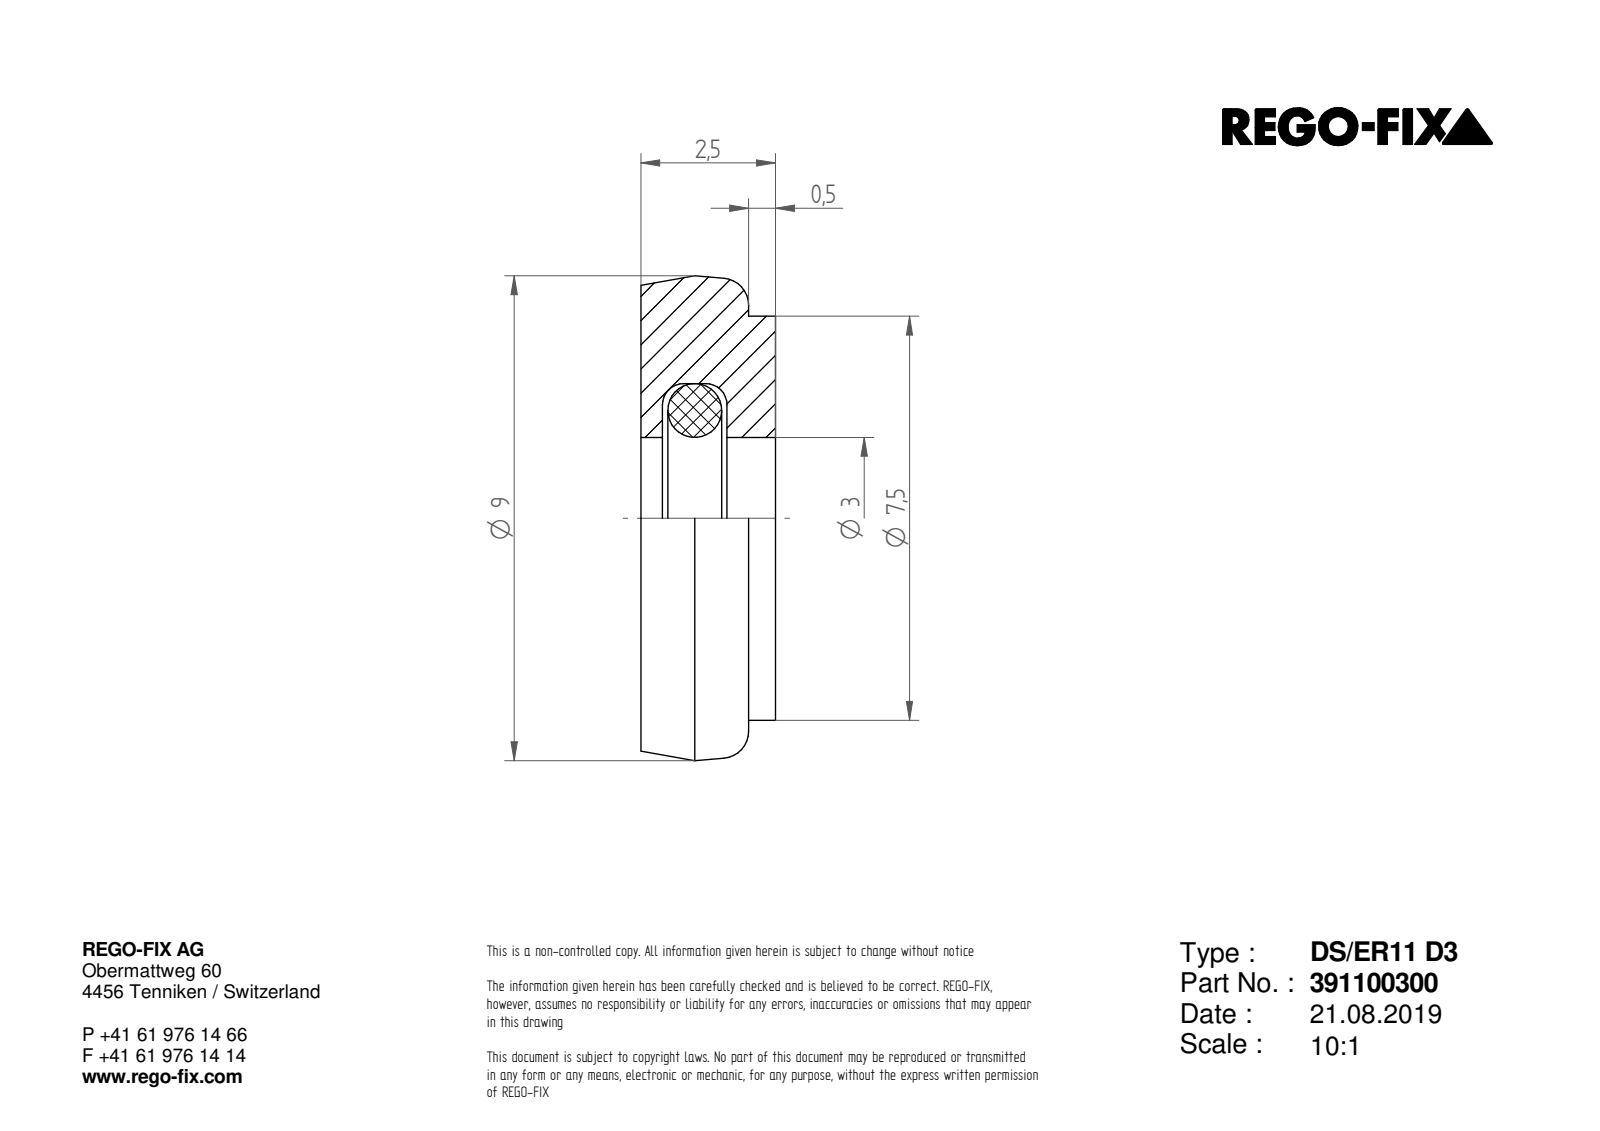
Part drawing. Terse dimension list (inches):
name: 0019587
written by: ST-DEVELOPER v16.7 (AUTOMOTIVE_DESIGN)
unit: in
bodies: 2 solids, 15 faces (5 planar, 4 cylindrical, 6 other)
size: 0.354 × 0.354 × 0.098
volume: 0.008 in³; area: 0.401 in²
holes: 1× ⌀0.118, 1× ⌀0.197
bosses: 1× ⌀0.295
face distances: 0.098, 0.016, 0.063, 0.083, 0.047, 0.035, 0.079, 0.02
